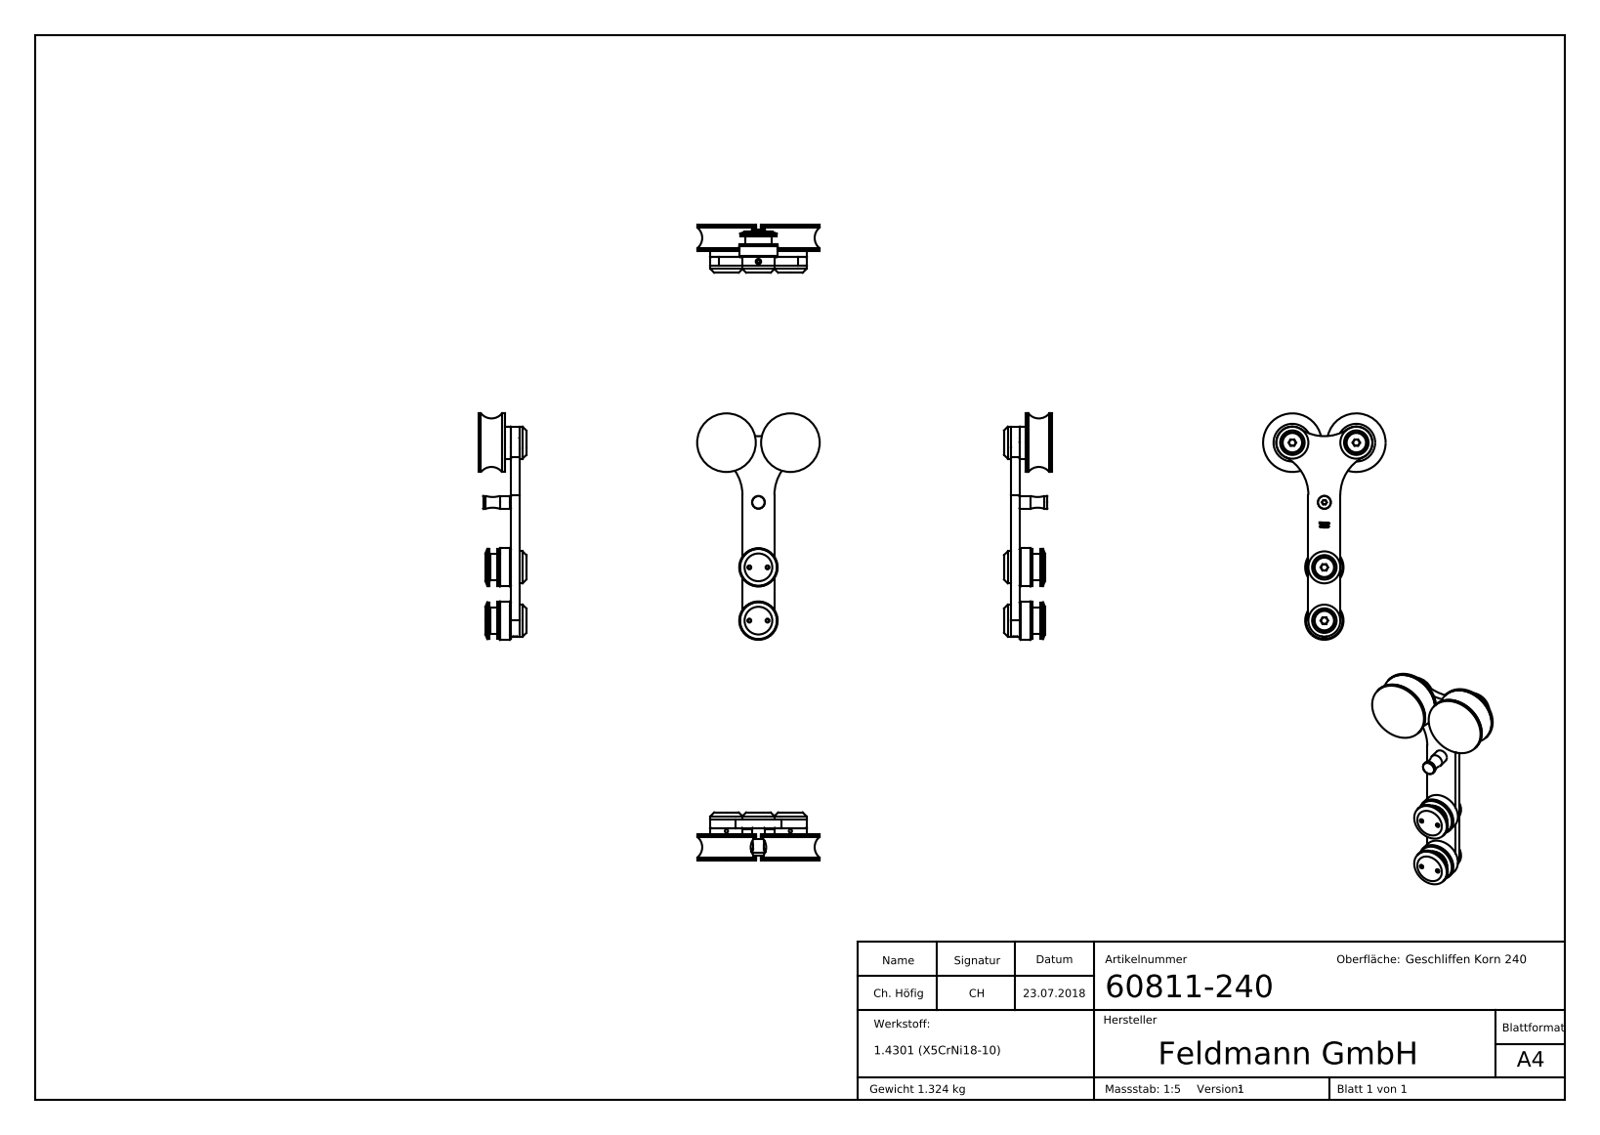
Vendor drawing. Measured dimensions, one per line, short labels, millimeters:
name: 6081X-240 Teil5_6081X-240 Teil5; DIN914_DIN 914 M5x8; 6081X-240 Teil2_6081X-240 Teil2; 6081X-240 Teil10_6081X-240 Teil10 (+8 more)
written by: SolidWorks 2015 (CONFIG_CONTROL_DESIGN)
unit: mm
bodies: 34 solids, 1348 faces (348 planar, 396 cylindrical, 604 other)
size: 212.5 × 115 × 45
volume: 206 673 mm³; area: 122 689 mm²
holes: 10× ⌀3, 4× ⌀1.7, 4× ⌀8.5, 4× ⌀13, 4× ⌀18.2, 4× ⌀34, 2× ⌀10.2, 2× ⌀13.8, 2× ⌀17, 2× ⌀19, 2× ⌀22.65, 2× ⌀25.4
bosses: 4× ⌀35, 4× ⌀30, 4× ⌀20, 4× ⌀10, 2× ⌀55, 2× ⌀36, 2× ⌀34.5, 2× ⌀34.4
rounds: 4× R0.2, 4× R0.5, 4× R5.1, 3× R40, 2× R8.4, 2× R10.5
face distances: 2, 8, 20.5, 22.5, 36.4, 28.4, 6.5, 15.9, 38.4, 7.9
hole spacings: 8.5, 8.7, 9.28, 12.5, 19.26, 50.72, 60, 63.53
